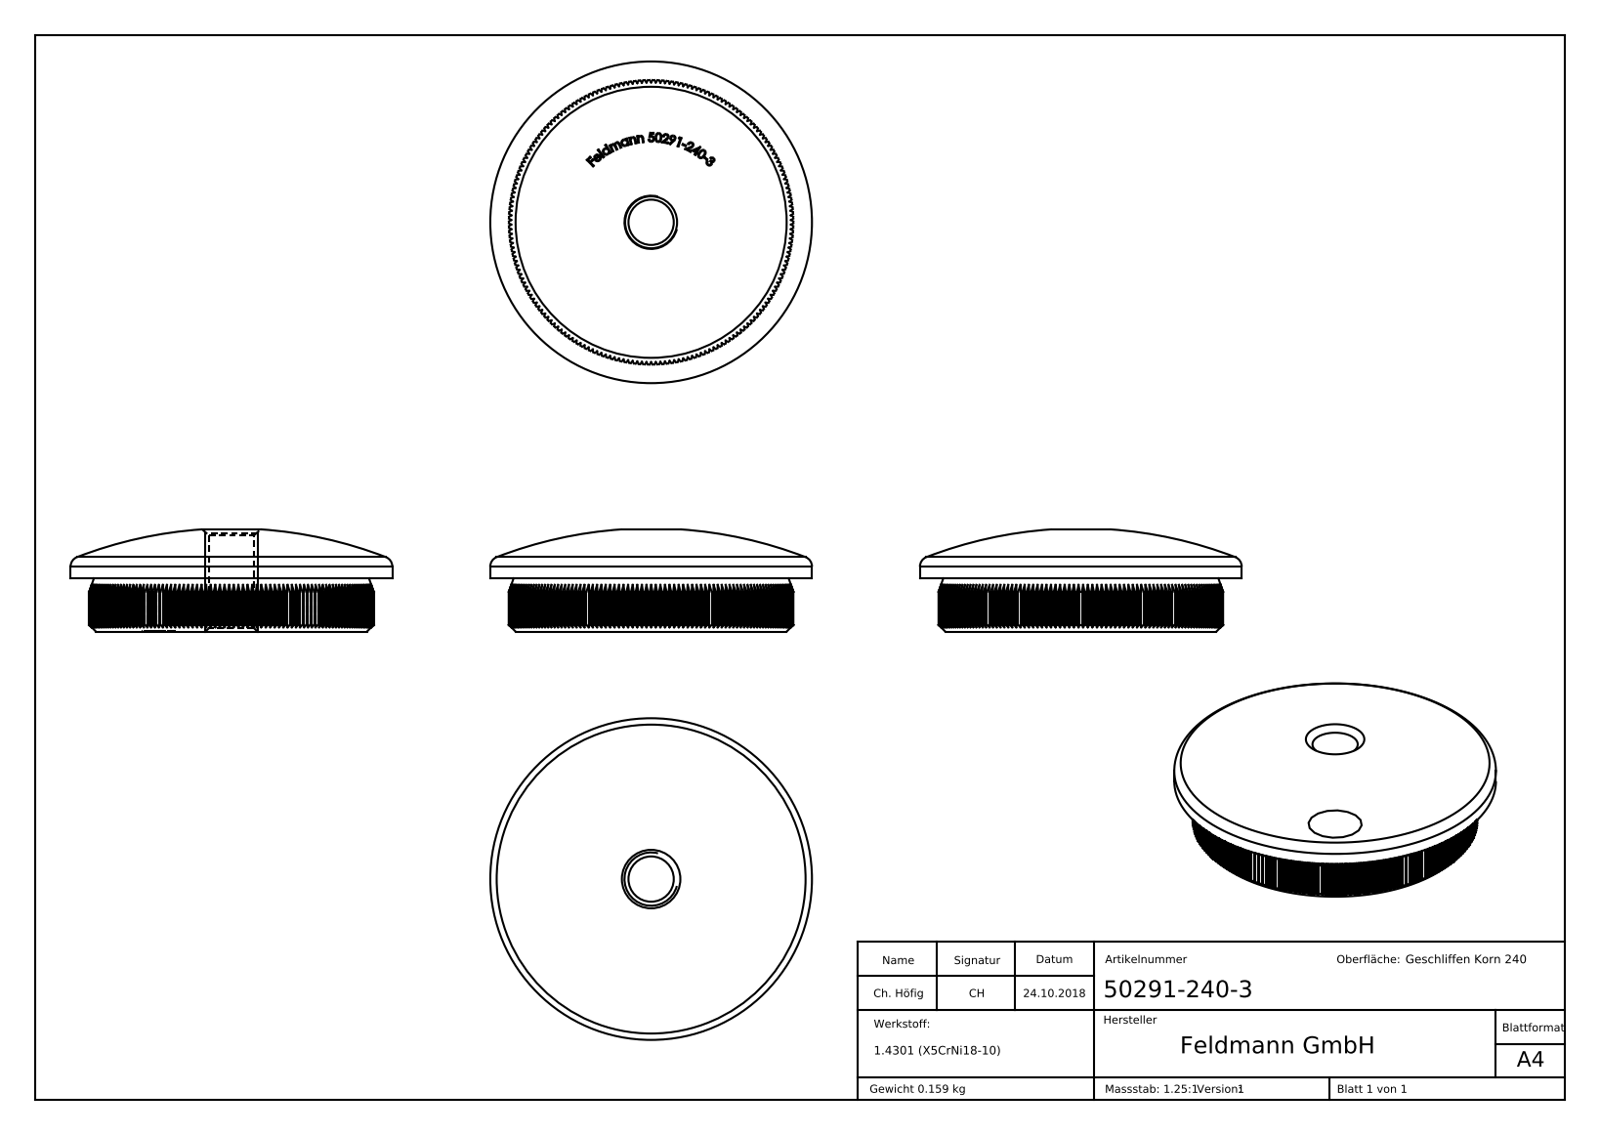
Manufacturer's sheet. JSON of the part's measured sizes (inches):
{"part_name": "50291-240-3", "step_written_by": "SolidWorks 2015 (CONFIG_CONTROL_DESIGN)", "units": "inches", "bodies": {"solids": 1, "faces": 813, "planar": 512, "cylindrical": 194, "other": 107}, "overall_size": [1.902, 1.902, 0.604], "volume_in3": 1.227, "surface_area_in2": 9.133, "round_holes": [[0.268, 1]], "round_bosses_or_shafts": [[1.902, 1]], "partial_cylinders_radius": [[0.841, 1]], "face_to_face_distances": [0.315, 0.827, 0.826, 0.828, 0.311, 0.026, 0.021, 0.026, 0.031, 0.028]}
